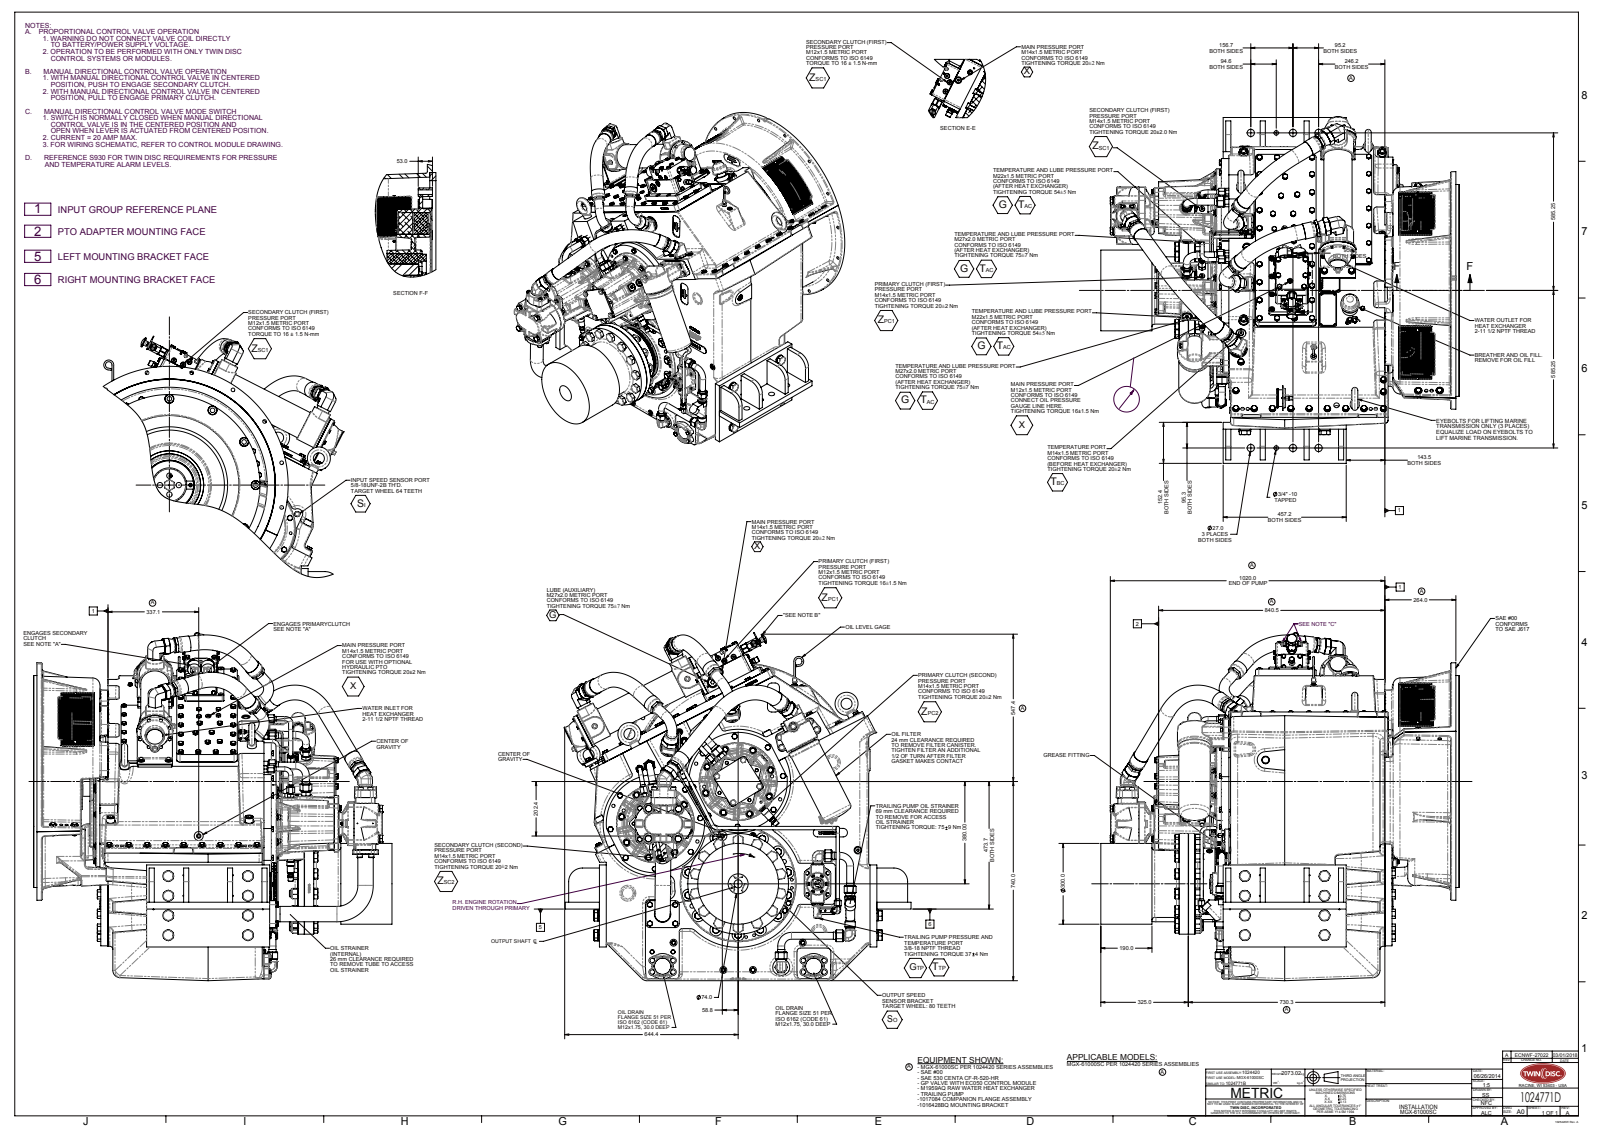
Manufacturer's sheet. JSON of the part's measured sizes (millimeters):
{"part_name": "1024771D", "step_written_by": "SolidWorks 2015 (AUTOMOTIVE_DESIGN)", "units": "millimeters", "bodies": {"solids": 0, "faces": 8571, "planar": 3950, "cylindrical": 1764, "other": 2857}, "overall_size": [1405.72, 1332, 1287.66], "round_holes": [[12, 25], [13.5, 21], [28, 19], [3, 15], [17, 12], [16.5, 9], [12.8, 7], [20, 7], [10, 6], [12.03, 6], [27, 6], [14, 5]], "round_bosses_or_shafts": [[24, 44], [18, 24], [36, 11], [19.05, 10], [40.01, 8], [27.46, 8], [25.4, 8], [18.9, 8]], "partial_cylinders_radius": [[12, 165], [3, 142], [6, 104], [43.44, 77], [3.05, 60], [2.54, 47], [1.5, 25], [1.52, 23]], "face_to_face_distances": [25.4, 1005.4, 6.41, 561.41, 555, 606.29, 599.88, 44.88, 30.79, 579.54], "hole_center_spacings": [30, 81.75, 50, 21.34, 141.6, 476, 10, 19]}
